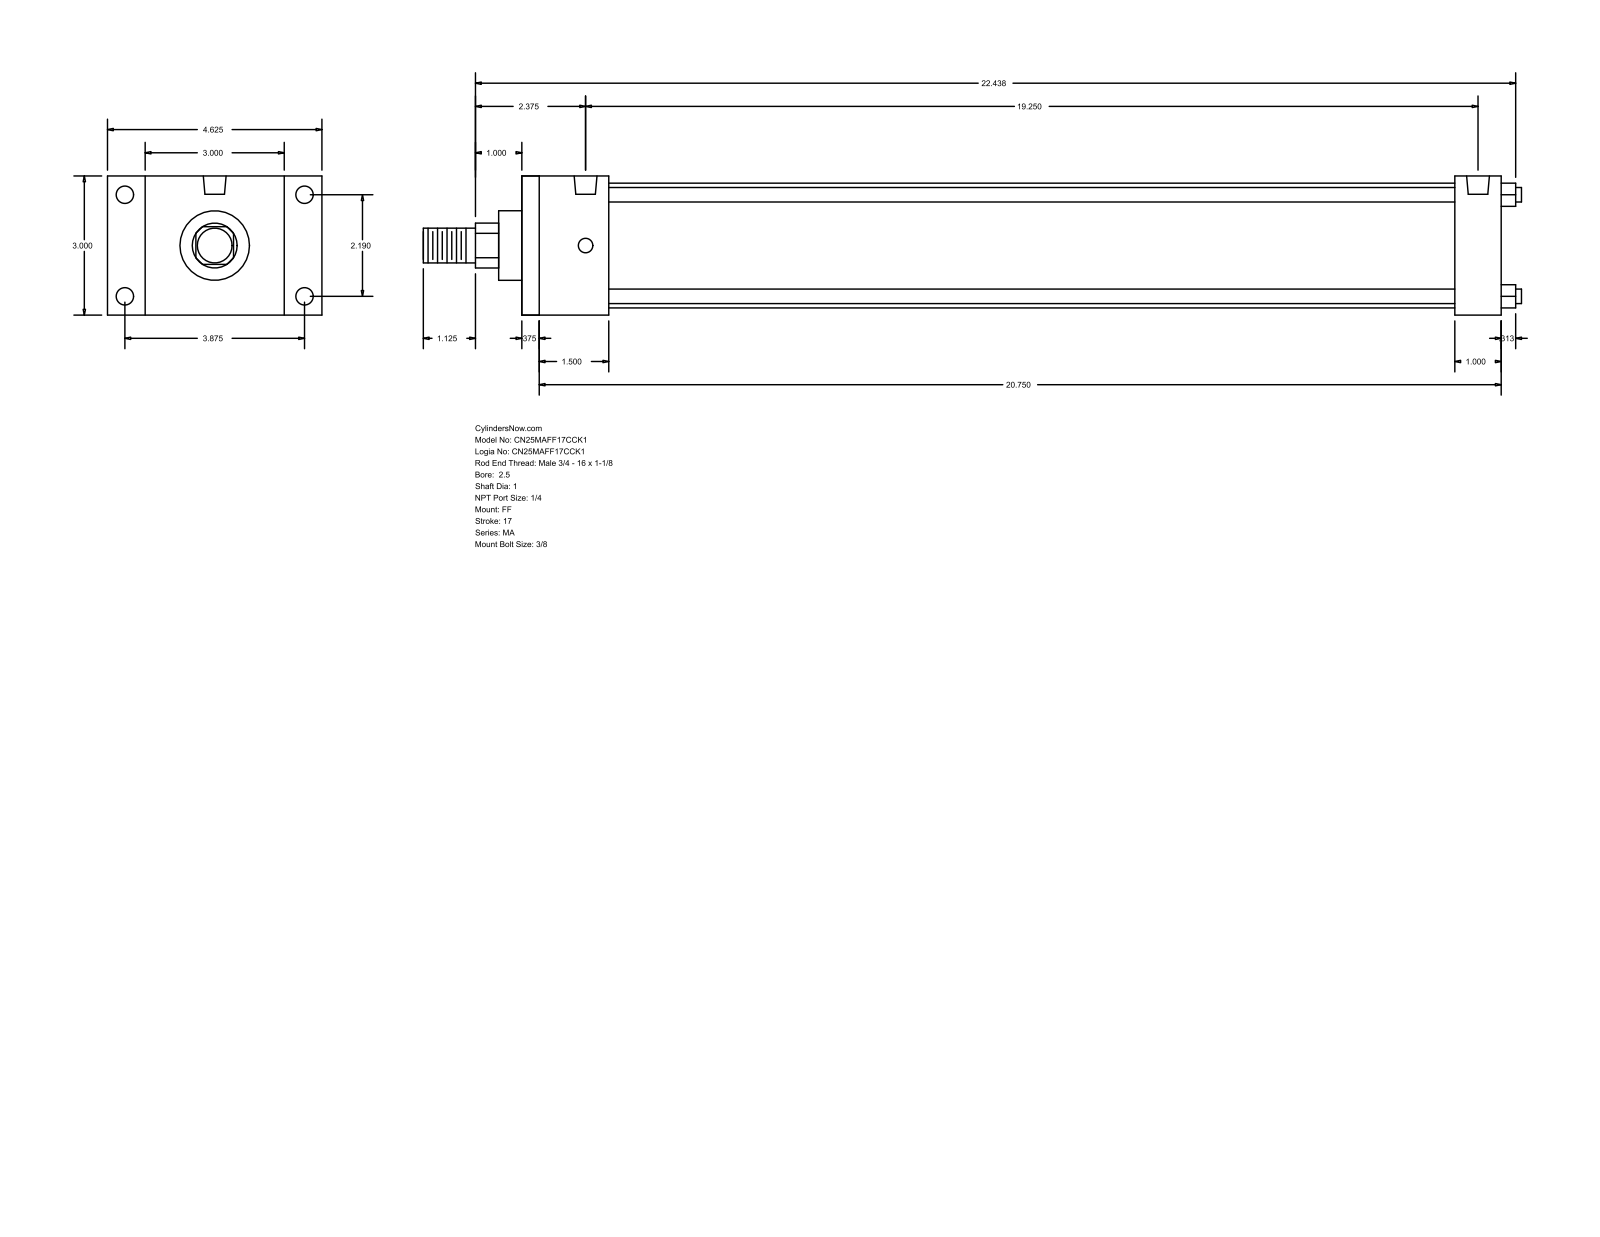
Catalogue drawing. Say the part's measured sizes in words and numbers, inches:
The part is named "MA_FF__0250_1". Its 3-D file was written by "GSSL Pune (CONFIG_CONTROL_DESIGN)". It is 0 solids with 92 faces: 64 planar, 28 cylindrical and 0 other. Overall it measures 23.687 by 4.625 by 3 inches. Round holes: 4 of diameter 0.313, 4 of diameter 0.375, 2 of diameter 0.492. Round bosses or shafts: 4 of diameter 0.313, 1 of diameter 2.69, 1 of diameter 1.5, 1 of diameter 1, 1 of diameter 0.75. Partial cylindrical surfaces (rounded edges, fillets, slot ends): 1 of radius 0.484. The main face-to-face distances are 3, 21.125, 0.375, 20.75, 1, 1.875, 20.125, 1.5, 19.75, 18.25. The hole center spacings are 2.19, 3.875, 4.451, 19.25.
